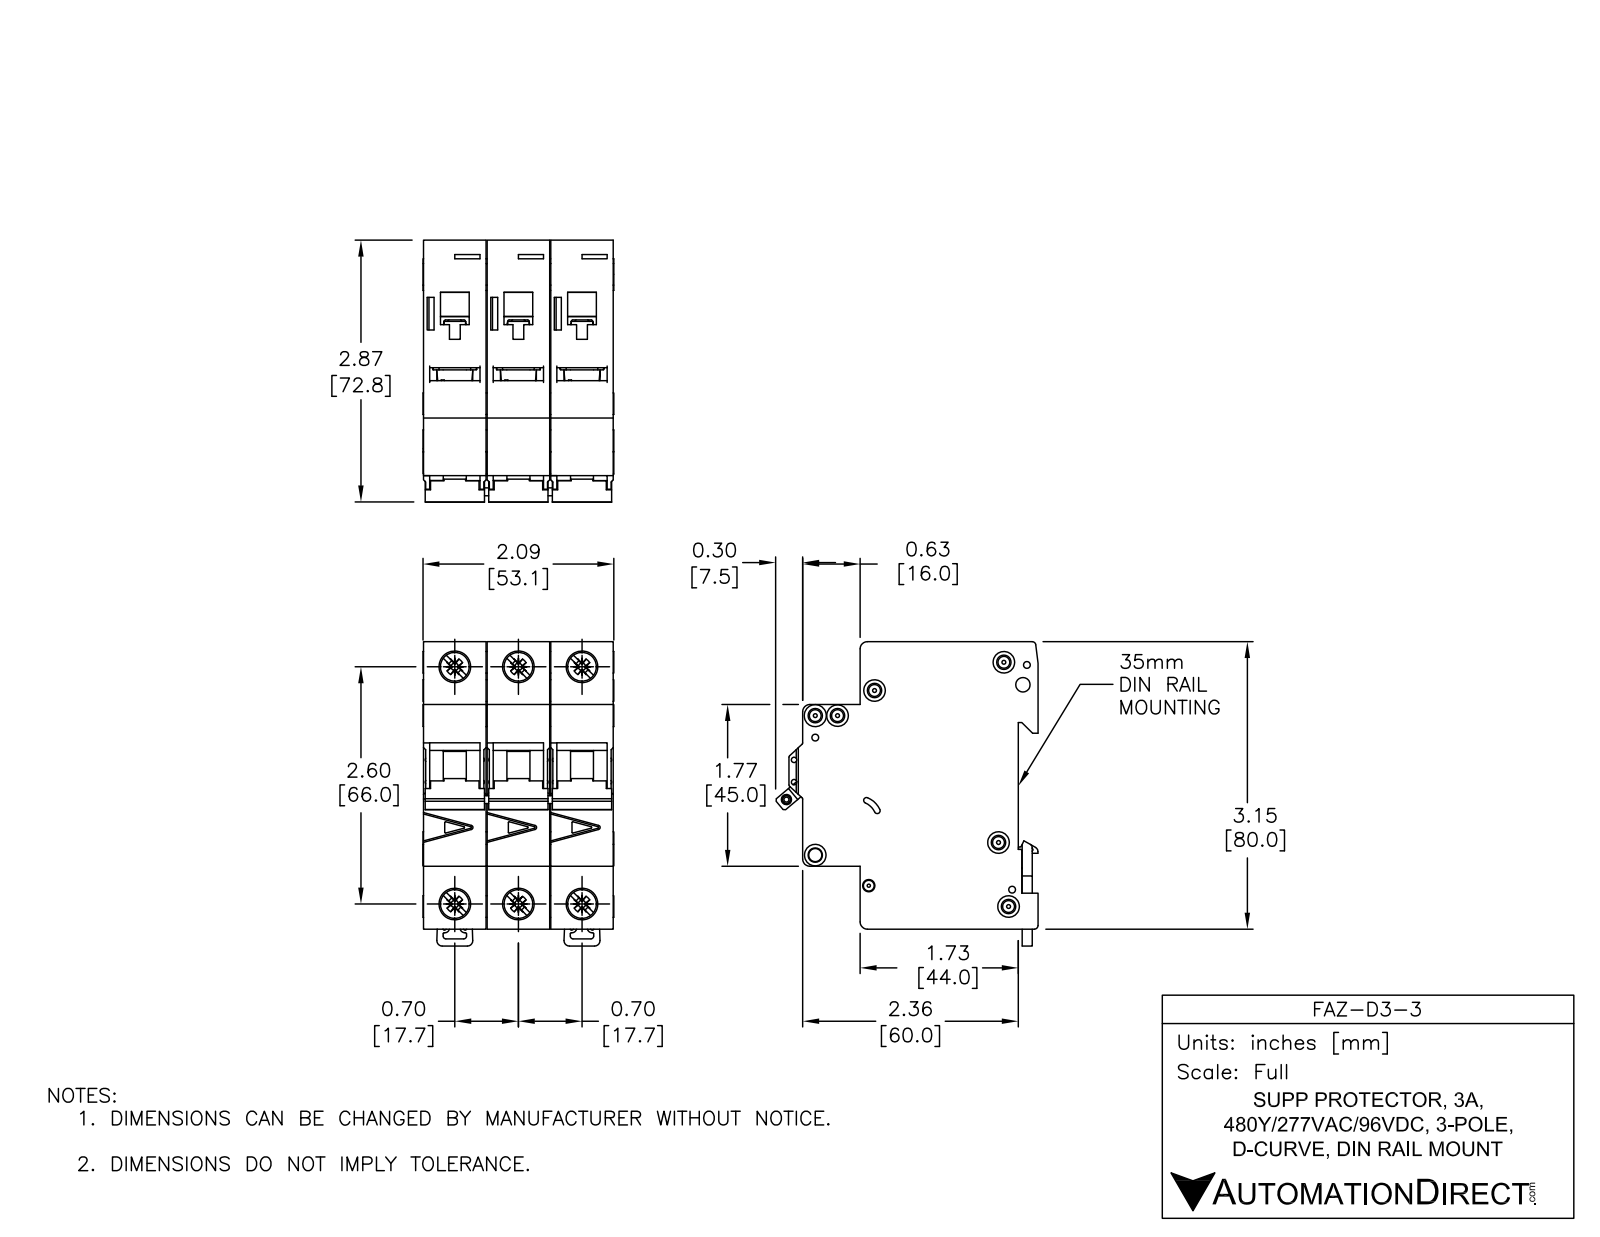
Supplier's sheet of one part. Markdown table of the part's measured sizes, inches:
| quantity | value |
| --- | --- |
| part name | FAZ-D3-3 |
| STEP written by | SolidWorks 2014 (AUTOMOTIVE_DESIGN) |
| units | inches |
| bodies | 11 solids, 1650 faces (697 planar, 590 cylindrical, 363 other) |
| overall size | 3.338 × 2.876 × 2.091 |
| volume | 13.71 in³ |
| surface area | 89.98 in² |
| round holes (diameter × count) | 0.142 × 6, 0.323 × 4, 0.075 × 3, 0.043 × 2, 0.059 × 2, 0.157 × 2, 0.281 × 2, 0.085 × 1, 0.087 × 1, 0.1 × 1, 0.13 × 1, 0.134 × 1 |
| round bosses / shafts (diameter × count) | 0.236 × 4, 0.098 × 3, 0.323 × 2 |
| partial cylindrical surfaces (radius × count) | 0.01 × 68, 0.02 × 25, 0.039 × 12, 0.079 × 12, 0.008 × 11, 0.071 × 3, 0.031 × 2, 0.118 × 2 |
| main face-to-face distances | 0.697, 0.689, 1.394, 1.386, 2.083, 0.705, 3.129, 0.217, 1.949, 1.732 |
| hole center spacings | 0.697, 2.69, 2.598, 0.244, 0.537, 1.394, 2.948, 0.189 |
